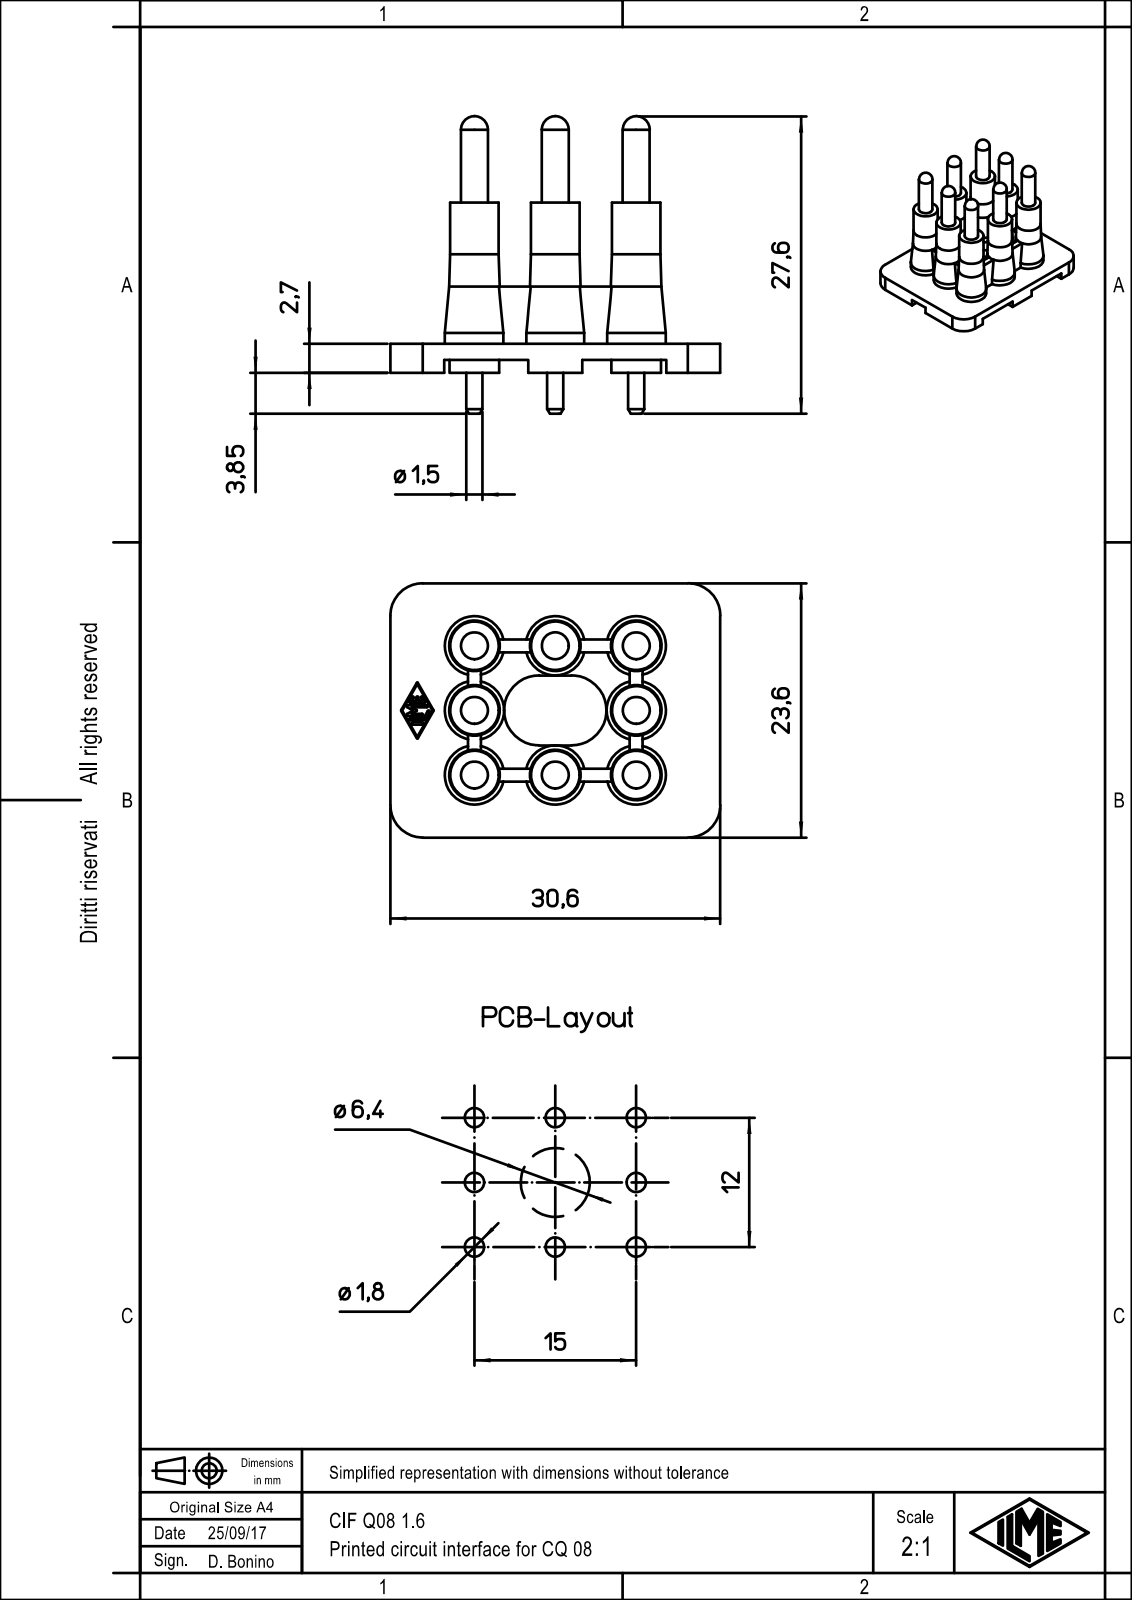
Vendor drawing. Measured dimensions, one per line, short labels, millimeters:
name: CIF_Q08_1.6
written by: PTC Creo Elements/Direct Modeling 19.0B 21-Mar-2015 (C) Parametric Technology GmbH (AUTOMOTIVE_DESIGN)
unit: mm
bodies: 1 solid, 242 faces (88 planar, 90 cylindrical, 64 other)
size: 30.6 × 27.6 × 23.6
volume: 3 576 mm³; area: 3 988 mm²
bosses: 8× ⌀5.5, 8× ⌀4.6, 8× ⌀4.5, 8× ⌀2.5, 8× ⌀1.5
rounds: 4× R1.8, 4× R3, 2× R3.25
face distances: 1.5, 1.2, 2.7, 15.8, 14.6, 13.1, 17.2, 5.2, 18.4, 6.4
